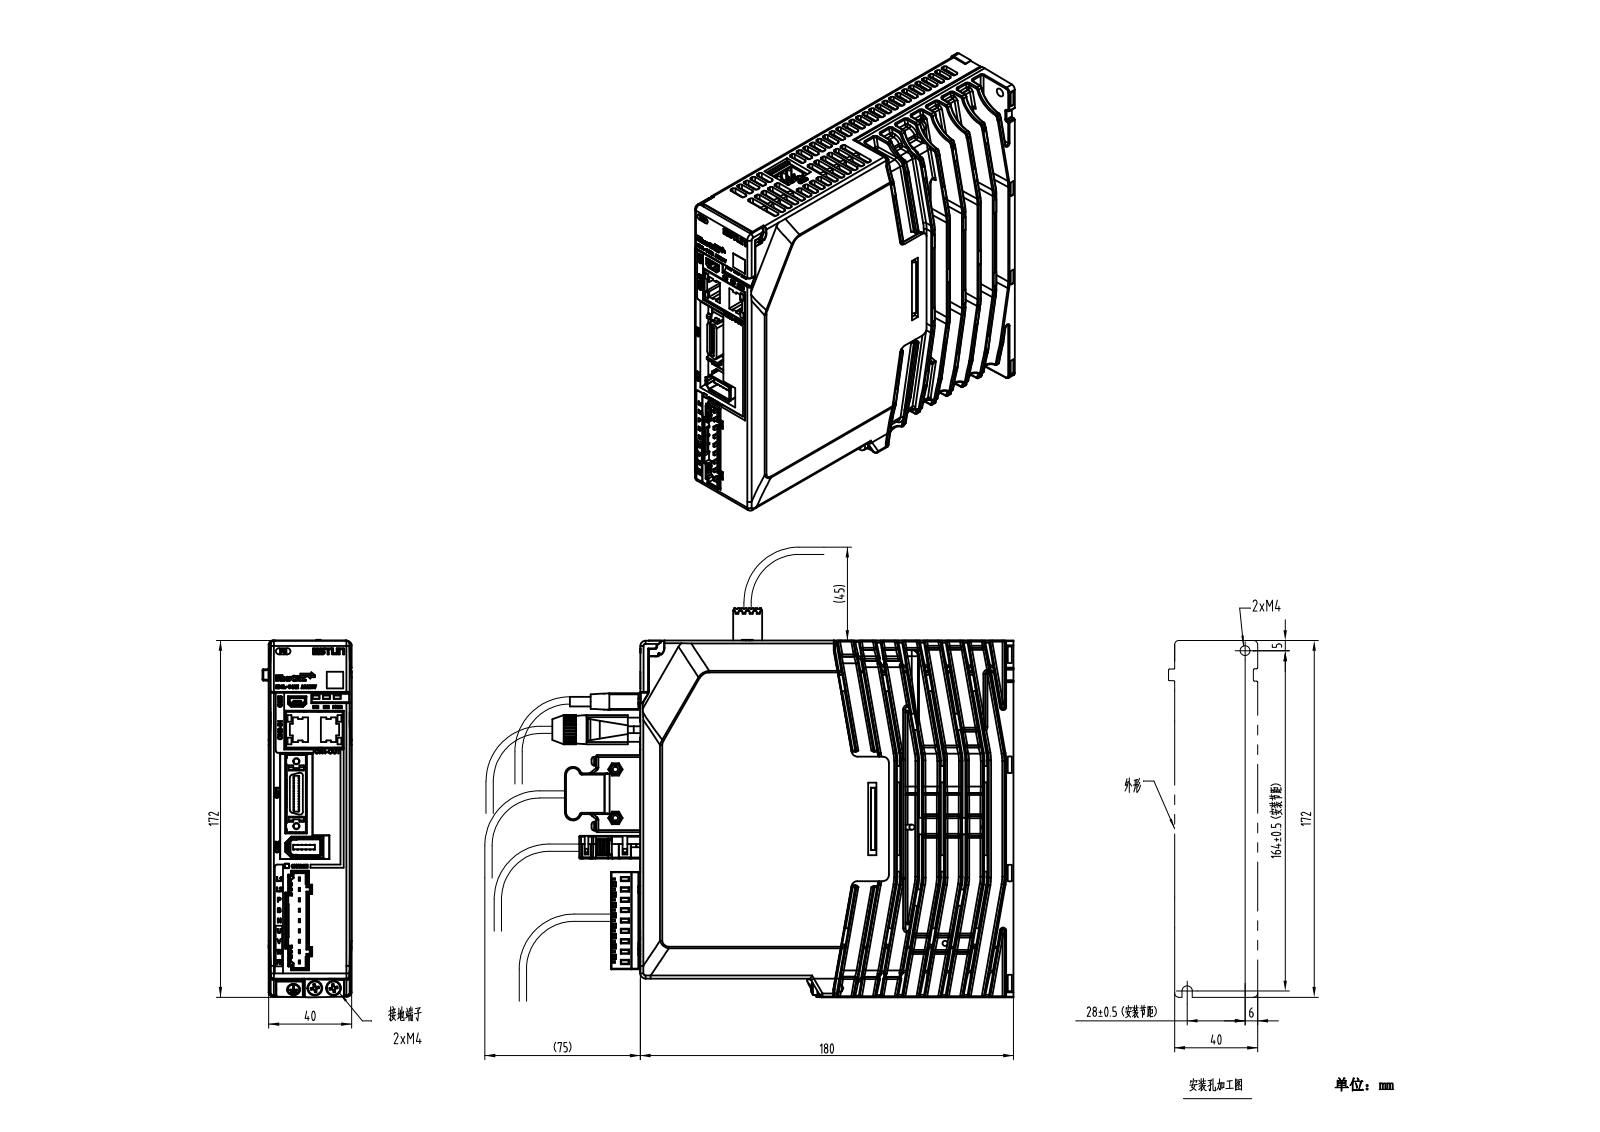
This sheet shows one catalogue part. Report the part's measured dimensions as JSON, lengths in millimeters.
{"part_name": "A结构STO", "step_written_by": "SolidWorks 2018 (CONFIG_CONTROL_DESIGN)", "units": "millimeters", "bodies": {"solids": 28, "faces": 9576, "planar": 6000, "cylindrical": 1652, "other": 1924}, "overall_size": [181, 172.3, 43], "volume_mm3": 349549, "surface_area_mm2": 286683, "round_holes": [[2, 7], [2.5, 7], [3.5, 7], [1.2, 3], [2.2, 3], [8, 3], [1.25, 2], [2.6, 2], [2.8, 2], [3.3, 2], [4.4, 2], [4.5, 2]], "round_bosses_or_shafts": [[1, 16], [0.5, 10], [4, 6], [2.3, 4], [7.27, 2], [6.8, 2], [6.73, 2], [2.5, 2]], "partial_cylinders_radius": [[0.5, 260], [1, 259], [0.15, 103], [0.2, 75], [0.3, 70], [4, 27], [3, 26], [1.5, 24]], "face_to_face_distances": [2, 8.5, 6.5, 31.5, 33.5, 40, 10.5, 8.3, 6.3, 10.33], "hole_center_spacings": [9.12, 34.69, 6.5, 148, 4.74, 5, 6.14, 12.36]}
